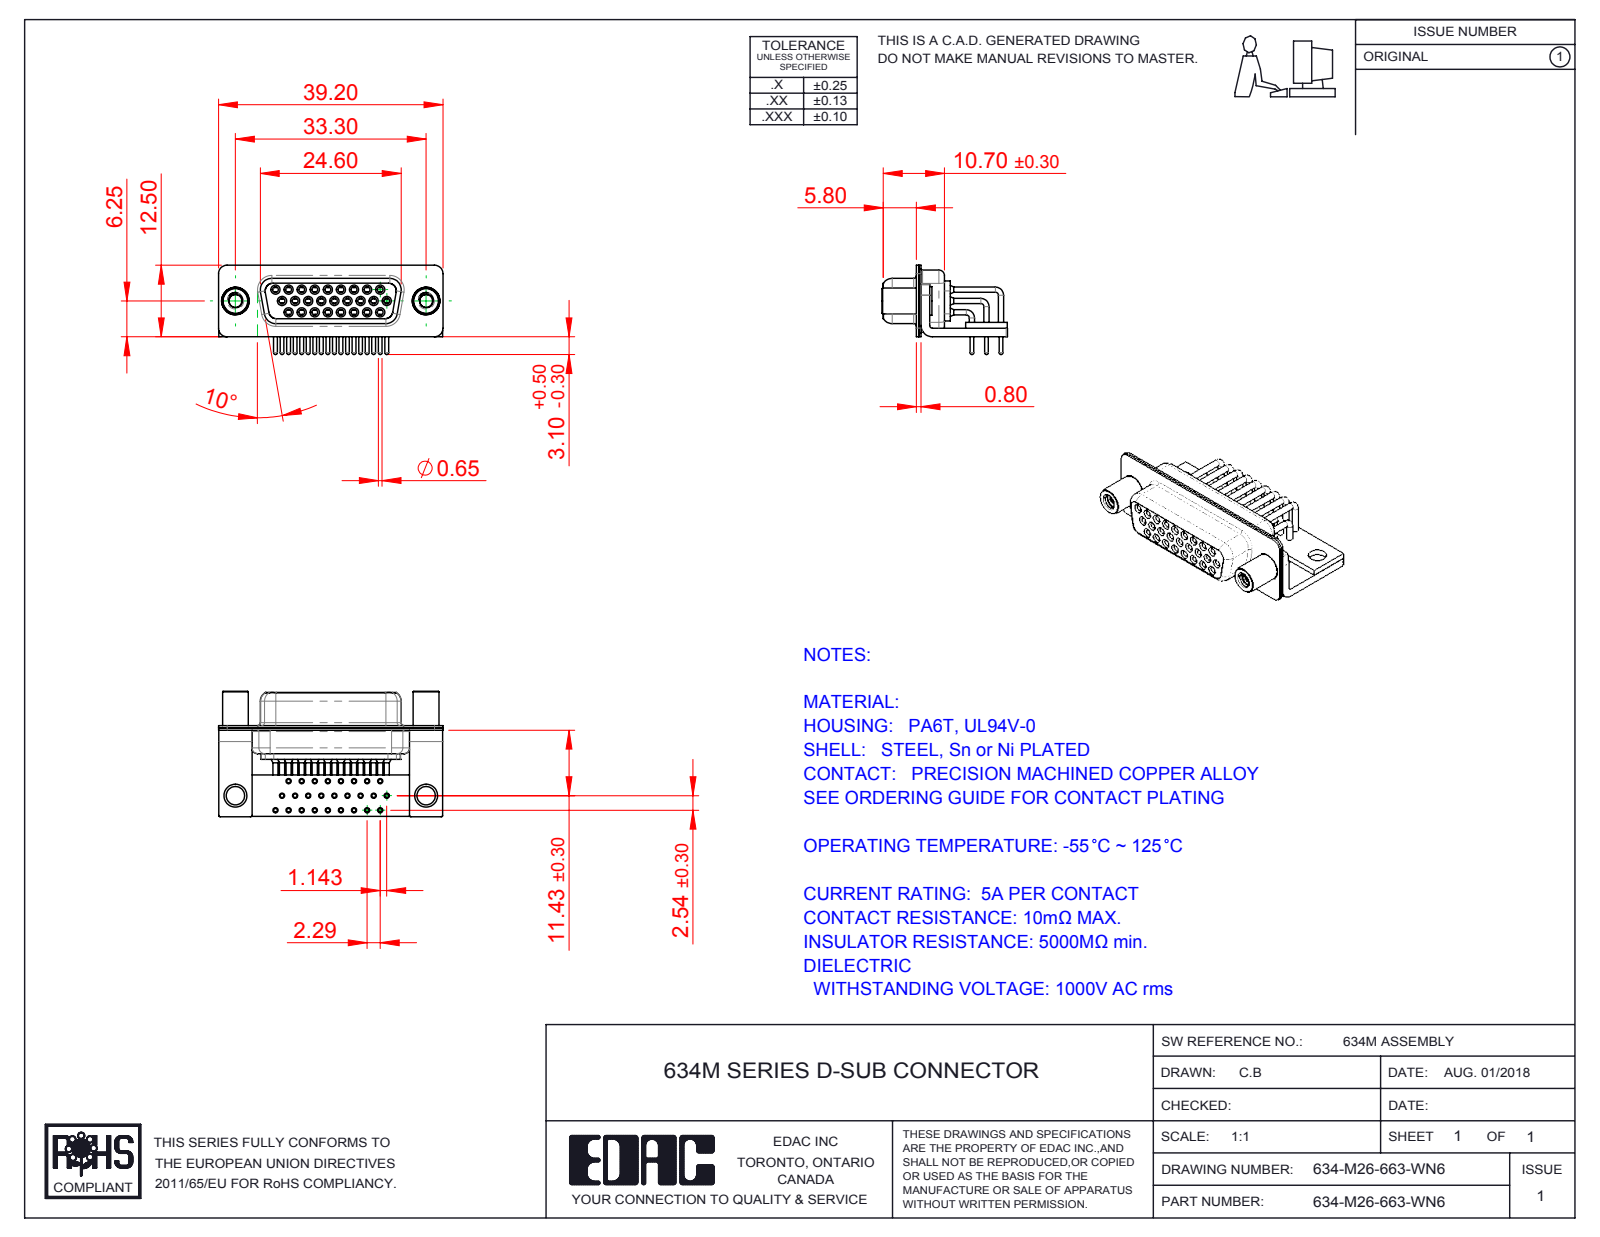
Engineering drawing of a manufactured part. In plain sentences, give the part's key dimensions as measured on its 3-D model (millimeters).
The part is named "634M Contact Row 2; 634M Contact Row 3; 634M 4-40 Threaded Standoff; 634-M26-663-WN6 (+6 more)". Its 3-D file was written by "SolidWorks 2016 (CONFIG_CONTROL_DESIGN)". It is 34 solids with 1809 faces: 485 planar, 851 cylindrical and 473 other. Overall it measures 39.2 by 21.9 by 15.6 millimeters. Its volume is 3 190 cubic millimeters and its surface area 10 090 square millimeters. Round holes: 26 of diameter 0.9, 26 of diameter 1, 26 of diameter 1.1, 26 of diameter 1.7, 26 of diameter 1.8, 26 of diameter 2, 2 of diameter 2.26, 2 of diameter 3.2, 2 of diameter 4, 2 of diameter 4.8. Round bosses or shafts: 27 of diameter 0.9, 26 of diameter 1.6, 26 of diameter 1.5, 26 of diameter 0.65, 2 of diameter 5, 2 of diameter 4.9, 2 of diameter 4.5, 1 of diameter 2. Partial cylindrical surfaces (rounded edges, fillets, slot ends): 16 of radius 0.25, 16 of radius 1.5, 13 of radius 2, 8 of radius 1.35, 8 of radius 1.6, 5 of radius 0.5, 4 of radius 0.6, 4 of radius 0.65. The main face-to-face distances are 0.4, 2.3, 1.9, 0.8, 1, 1.5, 9.35, 8.5, 1.45, 8.95. The hole center spacings are 4.57, 2.29, 2.28, 3.96, 6.05, 6.86, 4.27, 2.78.
